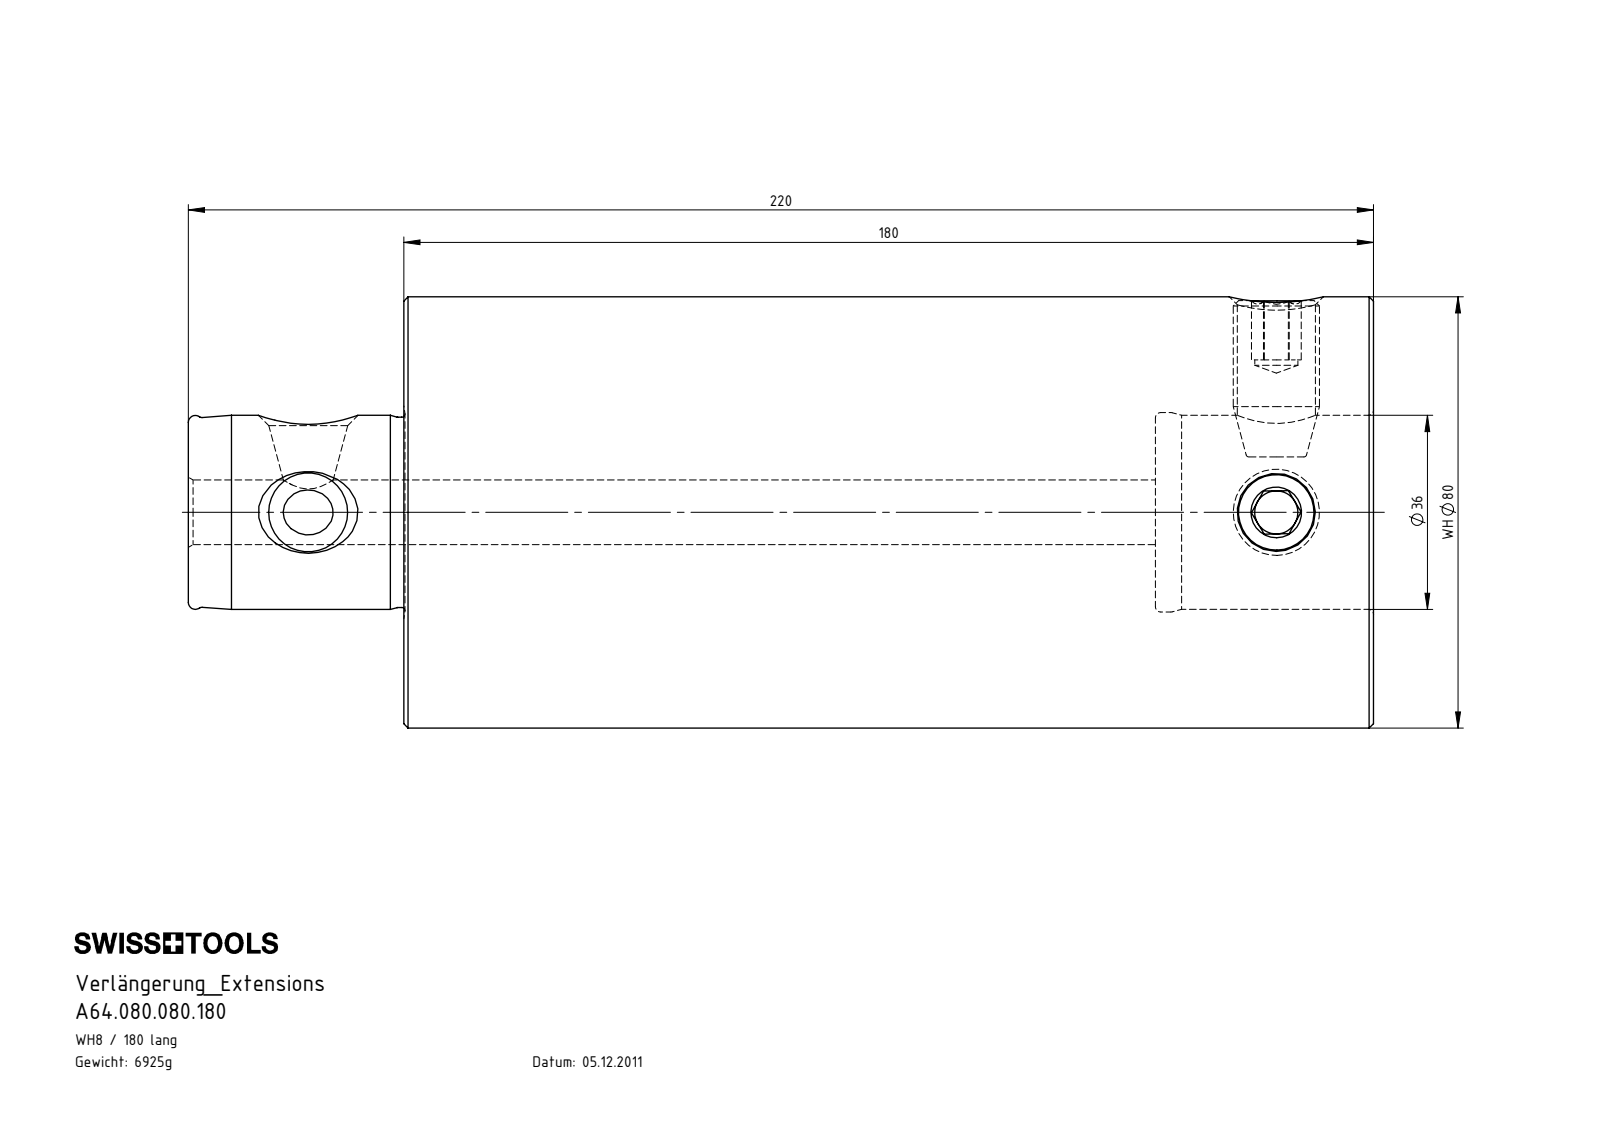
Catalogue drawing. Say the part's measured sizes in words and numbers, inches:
The part is named "WH8-ER1.001.029; WH8-WH8.001.180; WH8-WH8.001.180_A". Its 3-D file was written by "SolidWorks 2015 (AUTOMOTIVE_DESIGN)". It is 3 solids with 94 faces: 22 planar, 20 cylindrical and 52 other. Overall it measures 8.661 by 3.15 by 3.15 inches. Its volume is 53.84 cubic inches and its surface area 118.6 square inches. Round holes: 2 of diameter 0.571, 1 of diameter 0.472, 1 of diameter 1.417, 1 of diameter 1.457. Round bosses or shafts: 2 of diameter 0.63, 1 of diameter 3.15, 1 of diameter 1.39. The main face-to-face distances are 7.087, 5.492, 1.594, 1.575, 7.067, 8.661, 0.315, 1.142, 0.669, 0.472.
